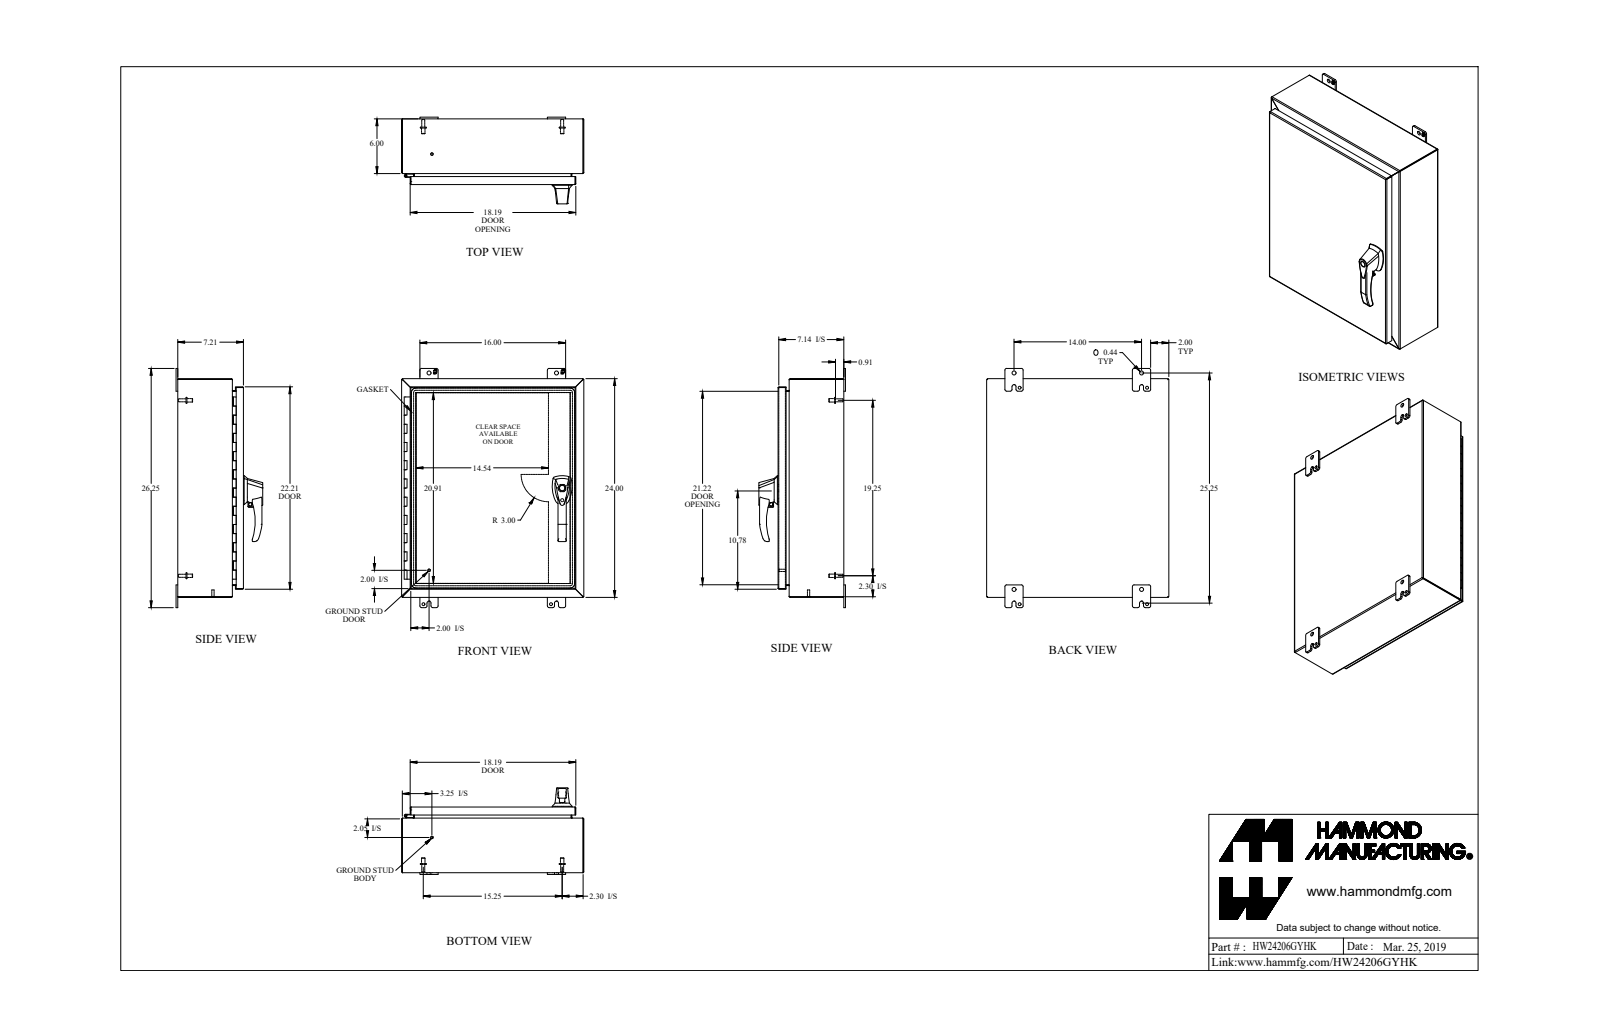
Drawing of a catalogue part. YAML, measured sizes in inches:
part_name: "HW24206GYHK"
step_written_by: "SolidWorks 2018 (AUTOMOTIVE_DESIGN)"
units: inches
bodies: {solids: 44, faces: 1450, planar: 725, cylindrical: 556, other: 169}
overall_size: [26.25, 20, 9.512]
volume: 156.3
surface_area: 3930
round_holes:
  - {diameter: 0.176, count: 6}
  - {diameter: 0.313, count: 4}
  - {diameter: 0.25, count: 3}
  - {diameter: 0.265, count: 3}
  - {diameter: 0.413, count: 3}
  - {diameter: 0.196, count: 2}
  - {diameter: 0.256, count: 2}
  - {diameter: 0.394, count: 2}
  - {diameter: 0.437, count: 2}
  - {diameter: 0.187, count: 1}
  - {diameter: 0.233, count: 1}
  - {diameter: 0.334, count: 1}
round_bosses_or_shafts:
  - {diameter: 0.375, count: 9}
  - {diameter: 0.25, count: 7}
  - {diameter: 0.156, count: 6}
  - {diameter: 0.65, count: 4}
  - {diameter: 0.33, count: 4}
  - {diameter: 1, count: 3}
  - {diameter: 0.63, count: 2}
  - {diameter: 0.51, count: 2}
partial_cylinders:
  - {radius: 0.25, count: 27}
  - {radius: 0.188, count: 24}
  - {radius: 0.036, count: 20}
  - {radius: 0.108, count: 20}
  - {radius: 0.06, count: 12}
  - {radius: 0.125, count: 9}
  - {radius: 0.045, count: 8}
  - {radius: 0.218, count: 8}
face_to_face_distances: [0.072, 0.072, 7.138, 7.066, 7.21, 7.138, 19.928, 23.928, 5.928, 19.856]
hole_center_spacings: [8.118, 8.119, 16.237, 1.111, 7.877, 8.119, 14, 19.224]
